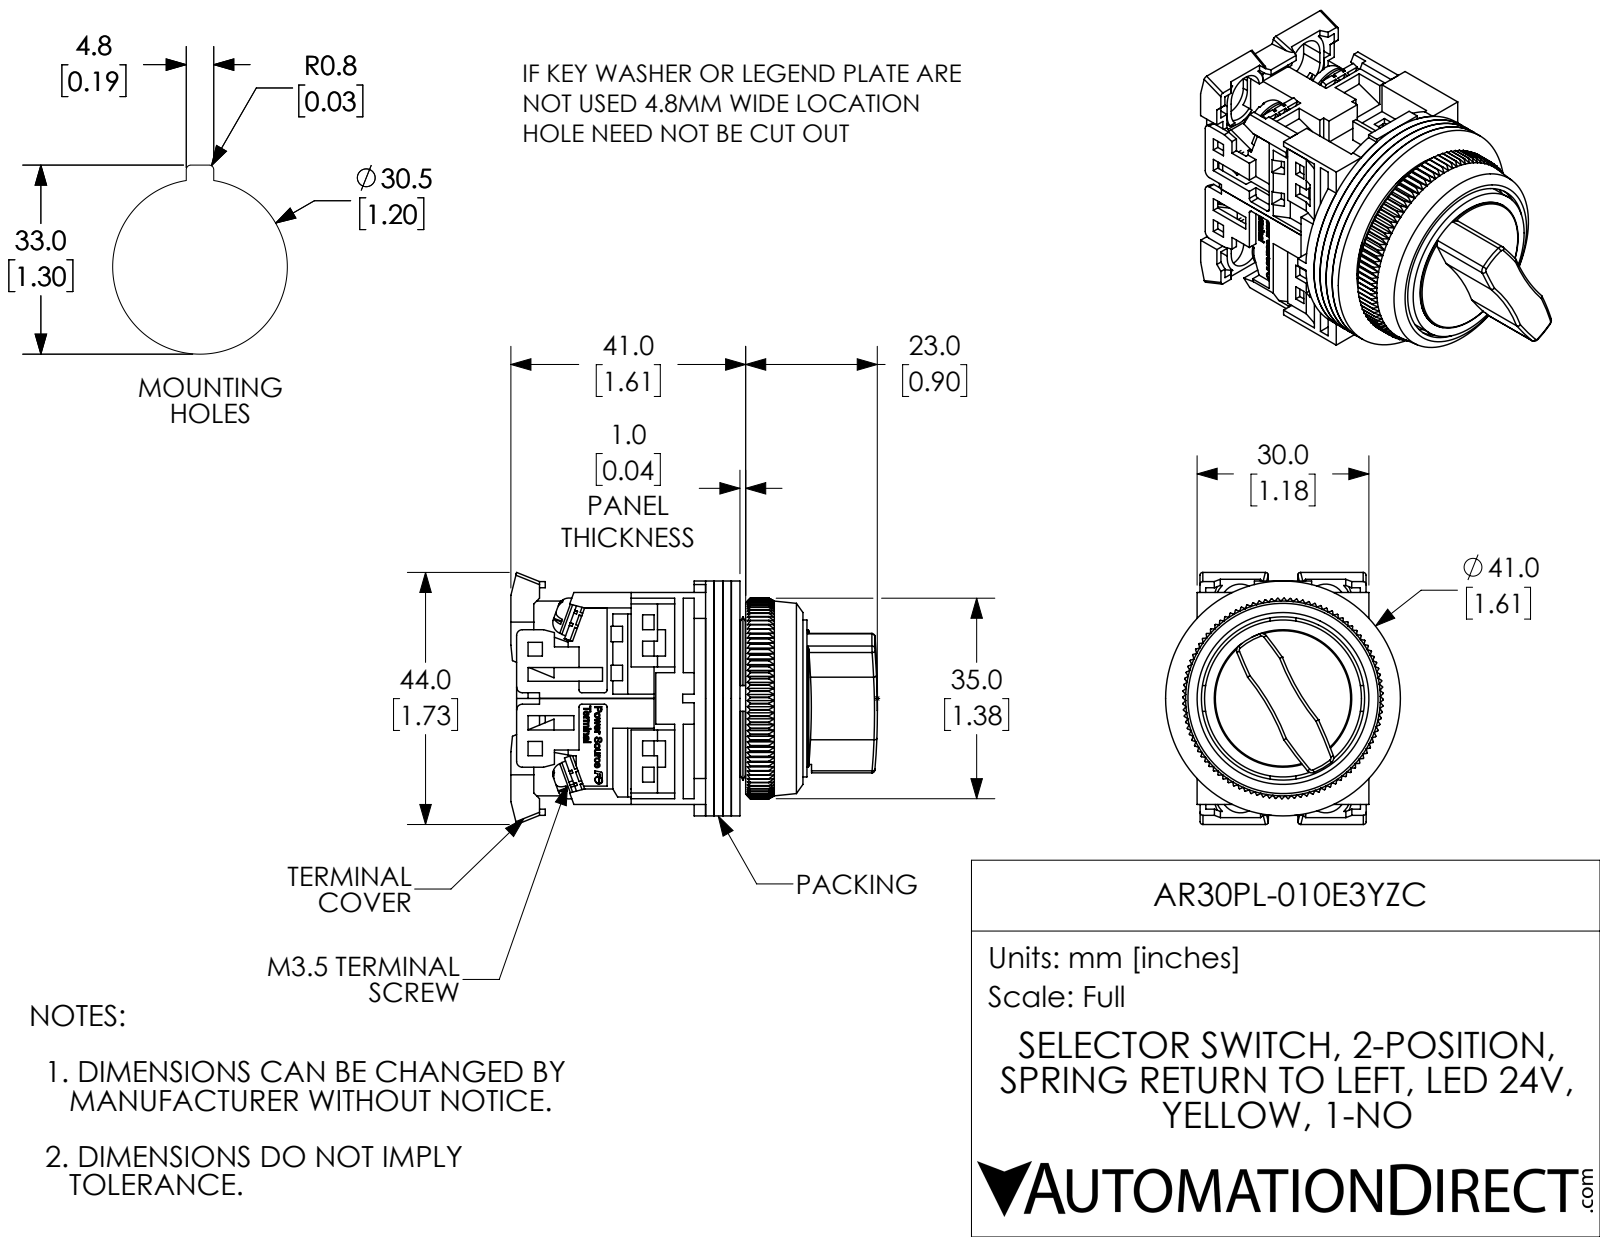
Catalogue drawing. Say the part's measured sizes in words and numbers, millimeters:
The part is named "AR30PL-010E3YZC". Its 3-D file was written by "SolidWorks 2017 (AUTOMOTIVE_DESIGN)". It is 25 solids with 2434 faces: 1731 planar, 305 cylindrical and 398 other. Overall it measures 64 by 44 by 41 millimeters. Its volume is 36 670 cubic millimeters and its surface area 38 260 square millimeters. Round holes: 8 of diameter 3.5, 4 of diameter 3.6, 1 of diameter 3, 1 of diameter 12, 1 of diameter 18, 1 of diameter 19.5, 1 of diameter 21, 1 of diameter 28.5, 1 of diameter 30, 1 of diameter 31.8. Round bosses or shafts: 4 of diameter 6.6, 4 of diameter 3.5, 2 of diameter 1.6, 1 of diameter 41, 1 of diameter 29.2, 1 of diameter 27.4, 1 of diameter 24, 1 of diameter 22.5. Partial cylindrical surfaces (rounded edges, fillets, slot ends): 16 of radius 1.5, 12 of radius 0.5, 8 of radius 1, 4 of radius 3.5, 4 of radius 4.5, 2 of radius 3, 2 of radius 40, 2 of radius 75. The main face-to-face distances are 1.5, 3, 4.5, 1, 2, 36, 34.5, 20.6, 5, 0.5. The hole center spacings are 14.7, 15.5.
